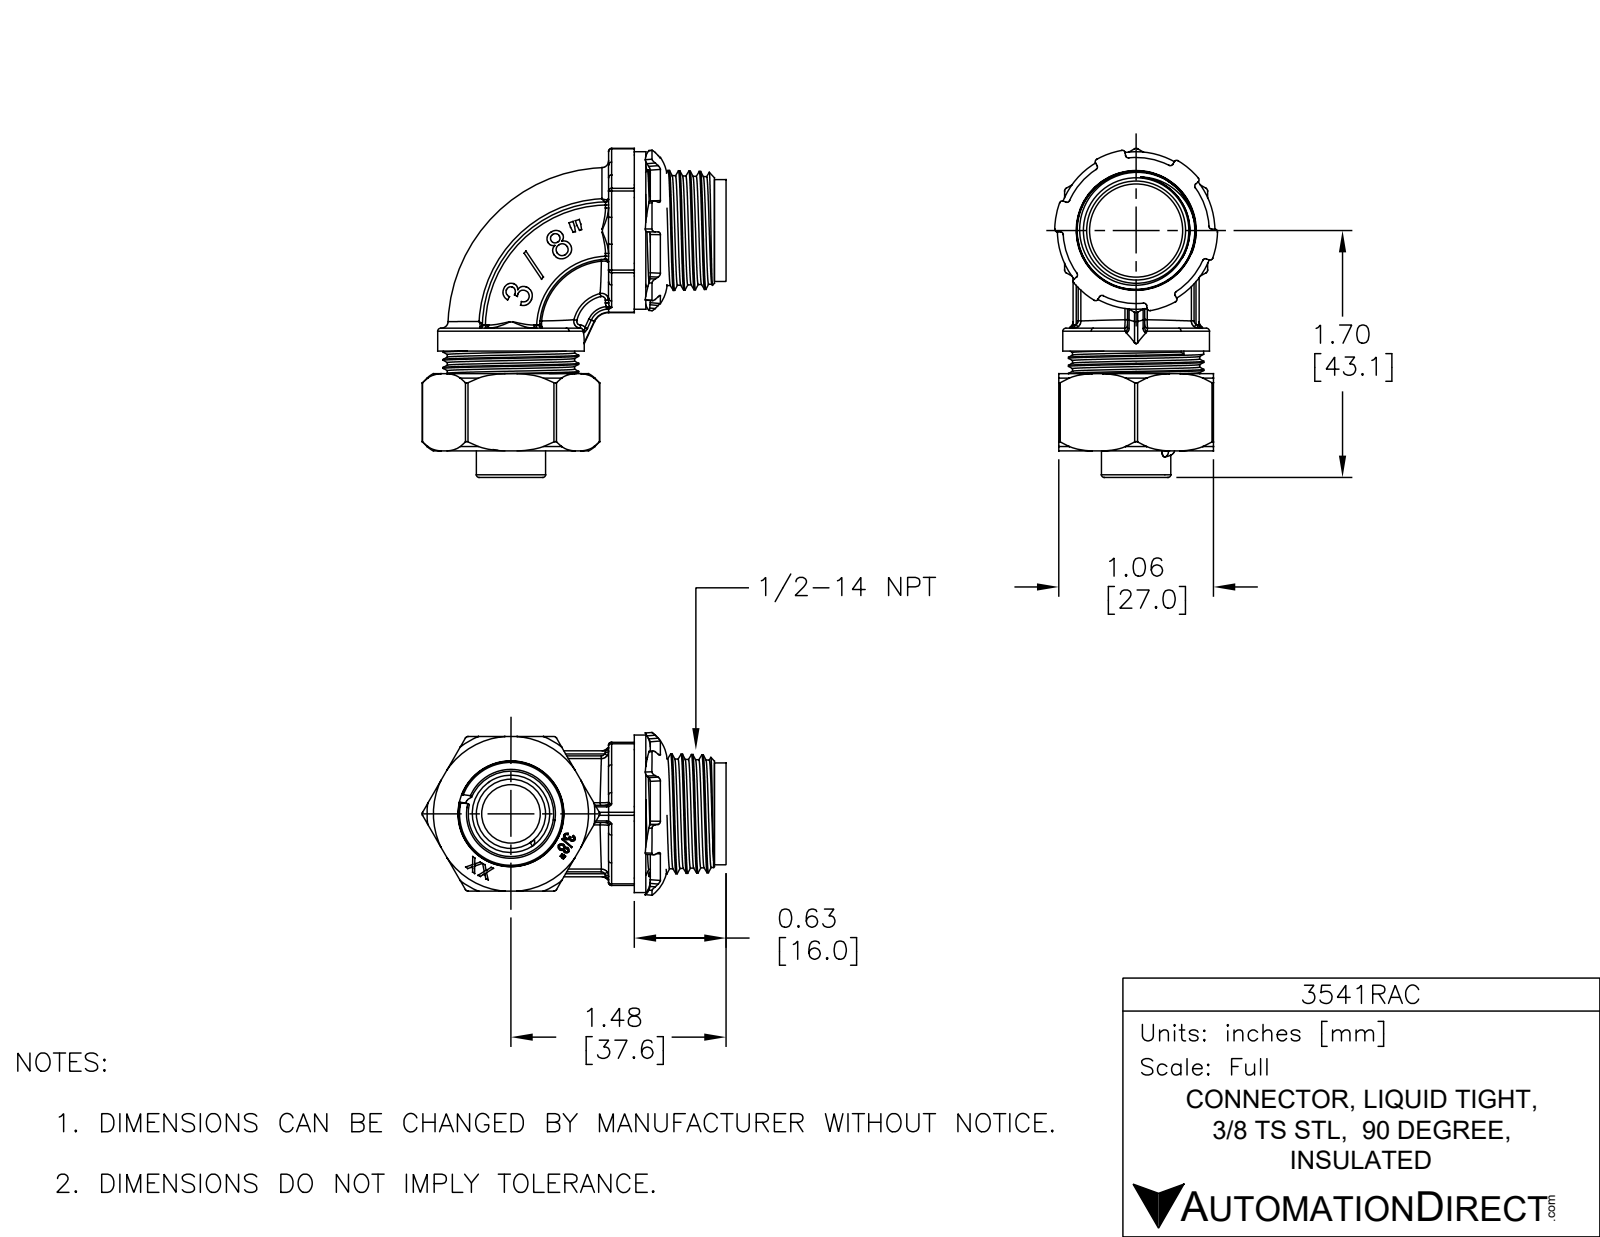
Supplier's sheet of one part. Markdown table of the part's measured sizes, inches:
| quantity | value |
| --- | --- |
| part name | 3541RAC-1; 3541RAC-2; 3541RAC-5; 3541RAC-4 (+4 more) |
| STEP written by | SolidWorks 2017 (AUTOMOTIVE_DESIGN) |
| units | inches |
| bodies | 8 solids, 851 faces (268 planar, 147 cylindrical, 436 other) |
| overall size | 2.262 × 2.094 × 1.119 |
| volume | 0.929 in³ |
| surface area | 29.85 in² |
| round holes (diameter × count) | 0.669 × 2, 0.1 × 1, 0.402 × 1, 0.44 × 1, 0.567 × 1, 0.64 × 1, 0.728 × 1, 0.732 × 1, 0.787 × 1, 0.858 × 1, 0.906 × 1 |
| round bosses / shafts (diameter × count) | 1.083 × 1, 1.008 × 1, 0.929 × 1, 0.866 × 1, 0.768 × 1, 0.701 × 1, 0.641 × 1, 0.476 × 1 |
| partial cylindrical surfaces (radius × count) | 0.021 × 23, 0.006 × 8, 0.02 × 6, 0.034 × 2, 0.008 × 1, 0.013 × 1, 0.334 × 1, 0.474 × 1 |
| main face-to-face distances | 1.063, 0.079, 0.866, 0.099, 0.965, 0.964, 0.098, 0.686, 0.059, 0.925 |
| hole center spacings | 0.453 |
